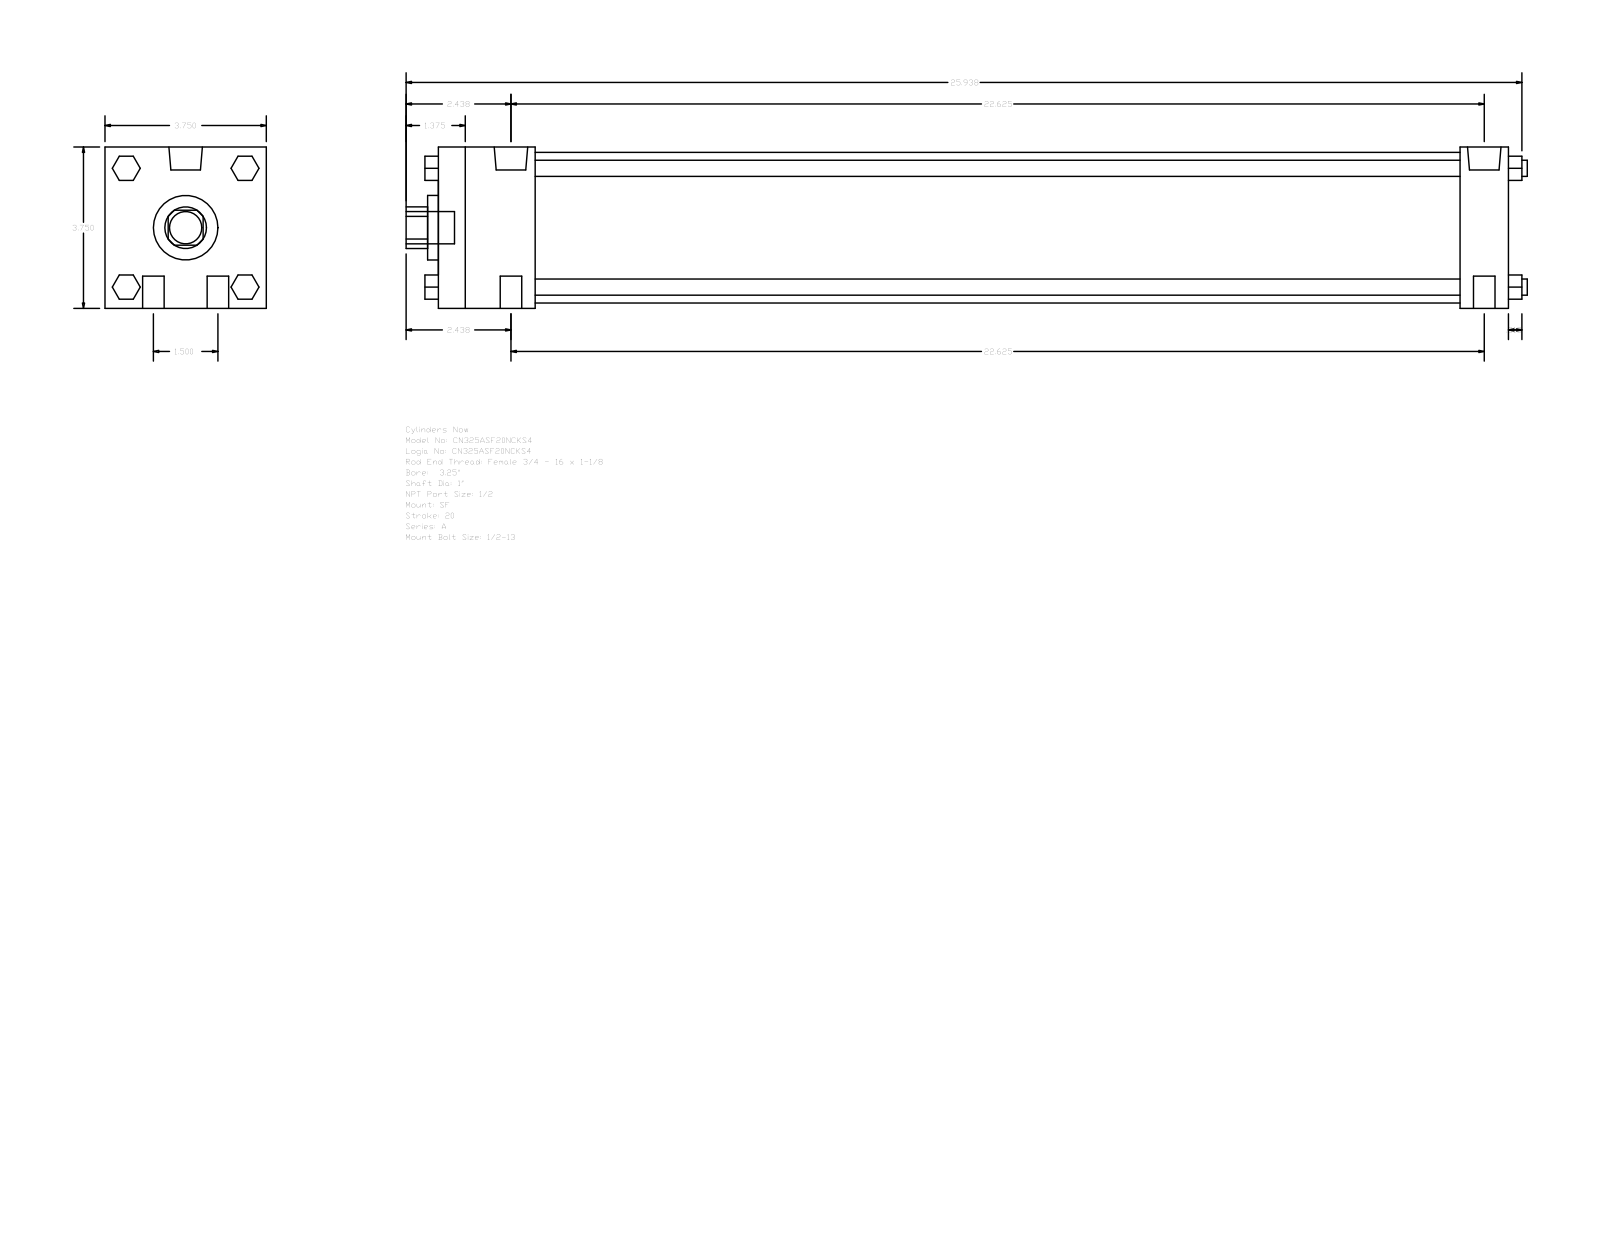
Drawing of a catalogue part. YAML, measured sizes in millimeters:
part_name: "A_SF__0325_1"
step_written_by: "GSSL Pune (CONFIG_CONTROL_DESIGN)"
units: millimeters
bodies: {solids: 0, faces: 124, planar: 94, cylindrical: 30, other: 0}
overall_size: [661.99, 95.25, 95.25]
round_holes:
  - {diameter: 25.4, count: 1}
  - {diameter: 38.1, count: 1}
  - {diameter: 88.9, count: 1}
round_bosses_or_shafts:
  - {diameter: 12.7, count: 4}
  - {diameter: 9.53, count: 4}
  - {diameter: 19.77, count: 2}
  - {diameter: 8.73, count: 2}
  - {diameter: 19.05, count: 1}
partial_cylinders:
  - {radius: 12.29, count: 1}
face_to_face_distances: [95.24, 631.83, 603.25, 28.58, 57.15, 546.1, 574.68, 14.28, 35.05, 60.71]
